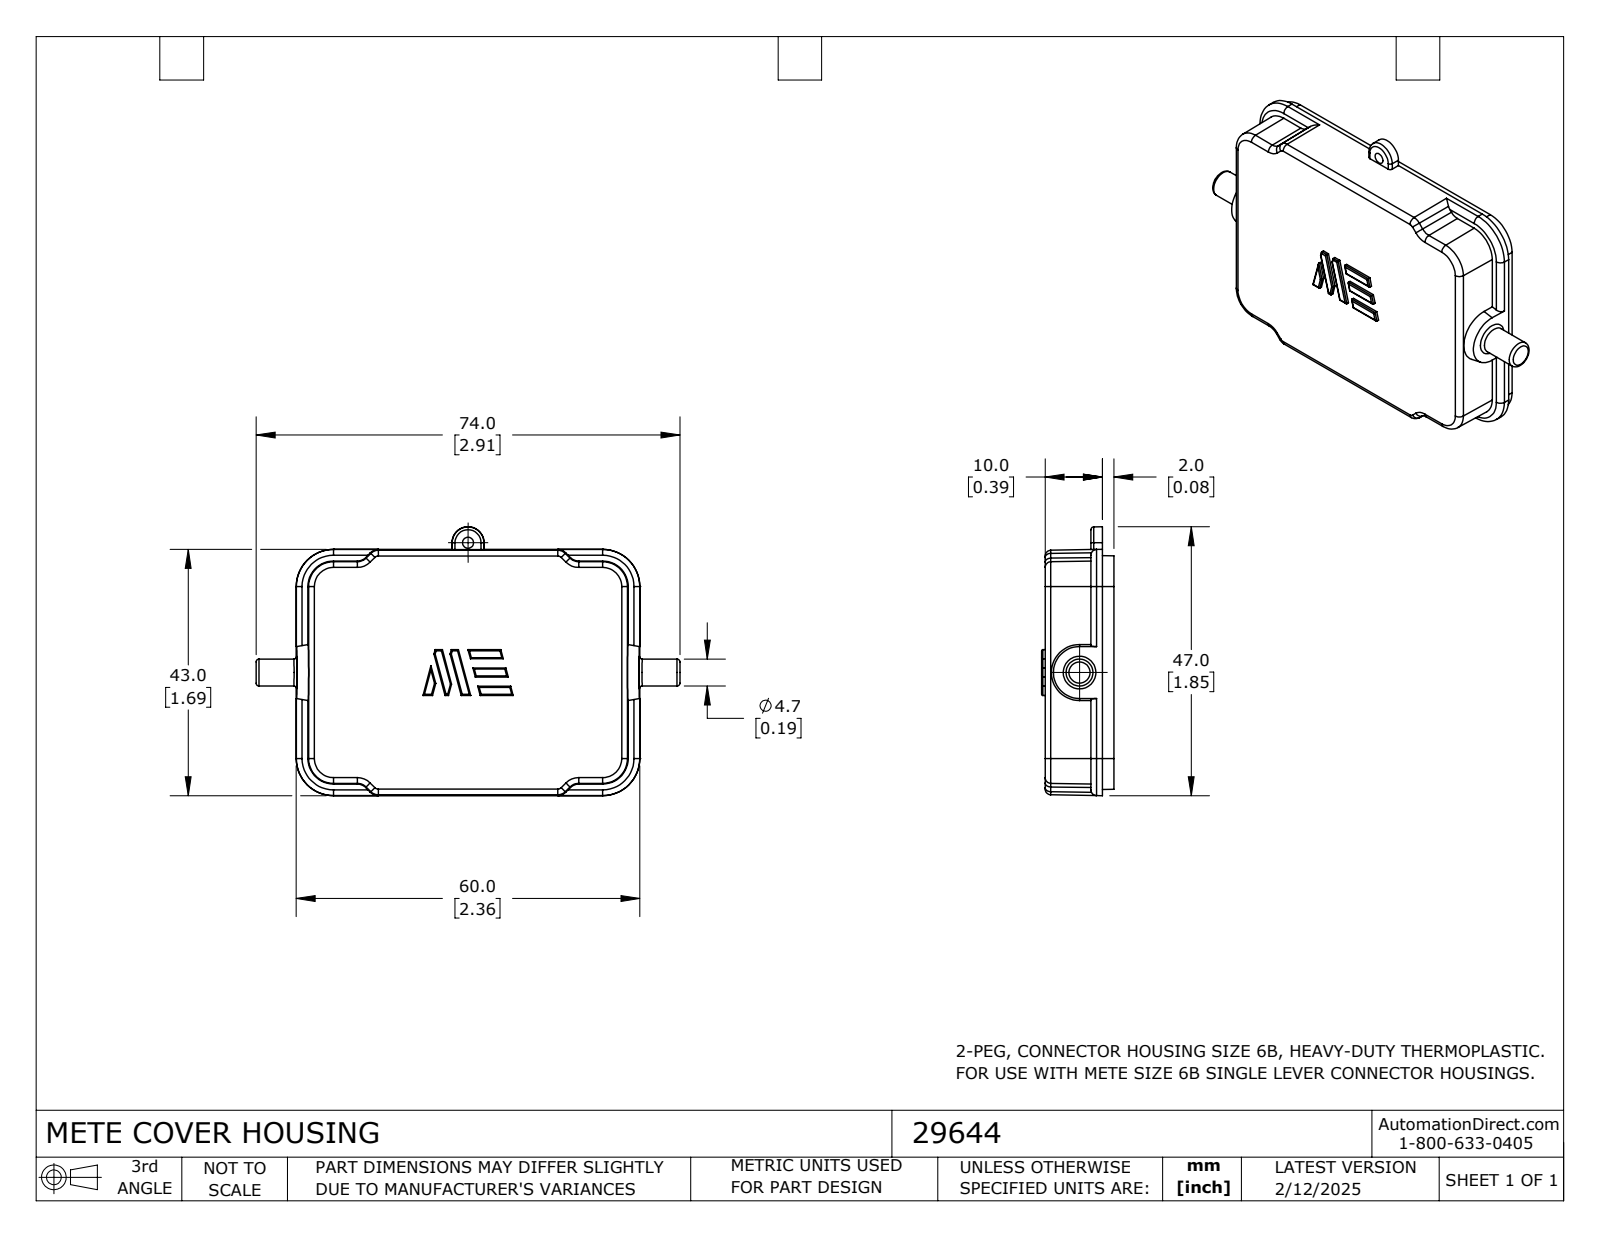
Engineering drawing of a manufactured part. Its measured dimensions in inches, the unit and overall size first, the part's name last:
Units: inches
Overall size (bounding box): 2.913 × 1.848 × 0.496
Round bosses / shafts (diameter × count): ⌀0.185 ×1
Partial cylindrical surfaces — rounded edges, fillets, slot ends (radius × count): R0.008 ×17, R0.039 ×14, R0.02 ×12
Main face-to-face distances: 0.079, 0.102, 0.394, 0.315, 0.067, 0.146, 0.043, 0.024, 0.472, 1.504
Volume: 0.549 in³ · Surface area: 14.2 in²
Bodies: 1 solid, 228 faces (84 planar, 65 cylindrical, 79 other)
Part name (STEP PRODUCT): 29644
STEP written by: SolidWorks 2024 (CONFIG_CONTROL_DESIGN)
